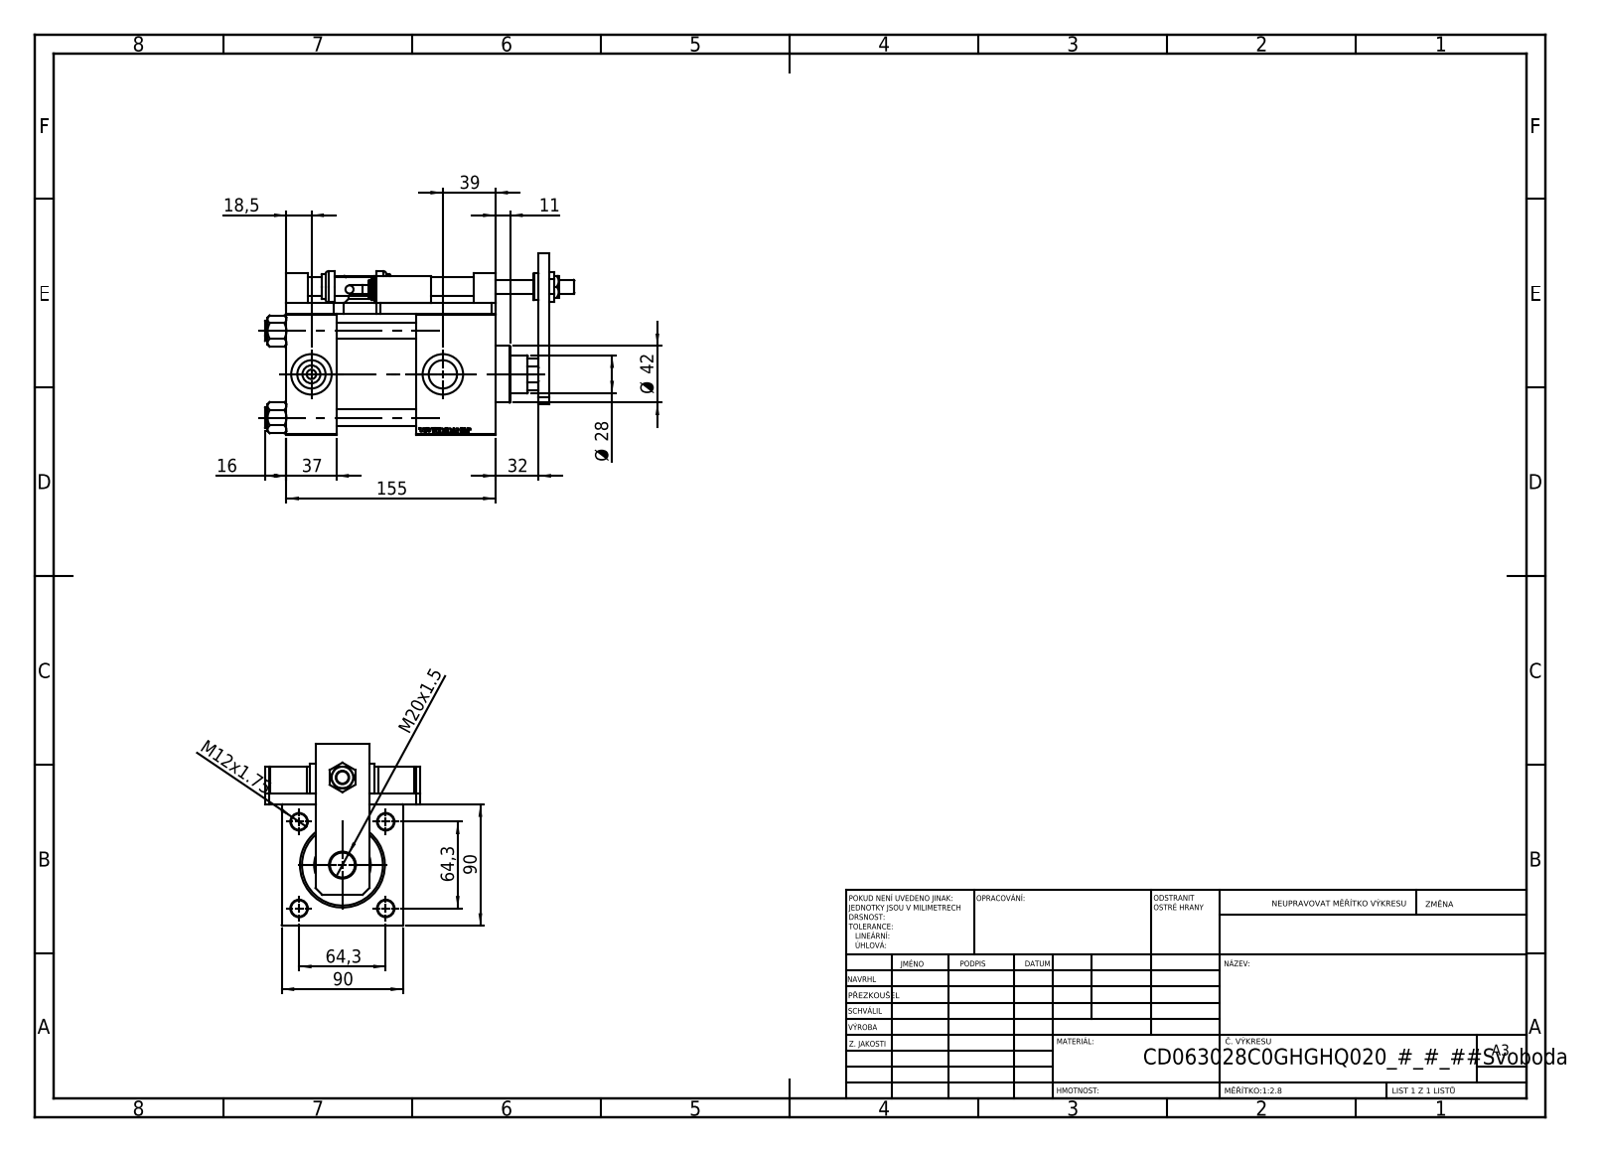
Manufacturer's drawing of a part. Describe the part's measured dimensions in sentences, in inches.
The part is named "V215CD_SWITCH_Q_PODLOZKA_BACK; V215CD_SWITCH_Q_NUT10; V215CD_VCP_C; V215CD_C_TYCINKA (+7 more)". Its 3-D file was written by "SolidWorks 2019 (CONFIG_CONTROL_DESIGN)". It is 24 solids with 1376 faces: 647 planar, 154 cylindrical and 575 other. Overall it measures 9.035 by 5.315 by 4.528 inches. Its volume is 73.96 cubic inches and its surface area 409.8 square inches. Round holes: 4 of diameter 0.335, 4 of diameter 0.472, 4 of diameter 0.531, 2 of diameter 0.276, 2 of diameter 0.825, 2 of diameter 1.181, 1 of diameter 0.394, 1 of diameter 0.551, 1 of diameter 0.728, 1 of diameter 0.787, 1 of diameter 1.102, 1 of diameter 1.22. Round bosses or shafts: 4 of diameter 0.591, 3 of diameter 0.787, 2 of diameter 0.63, 2 of diameter 0.551, 2 of diameter 0.236, 1 of diameter 2.717, 1 of diameter 1.654, 1 of diameter 0.906. Partial cylindrical surfaces (rounded edges, fillets, slot ends): 4 of radius 0.295, 1 of radius 0.531. The main face-to-face distances are 0.315, 3.543, 4.646, 2.323, 1.457, 3.858, 6.102, 0.787, 1.26, 1.575. The hole center spacings are 1.79, 2.531, 1.26, 1.809, 3.58, 4.029, 5.472, 5.616.
